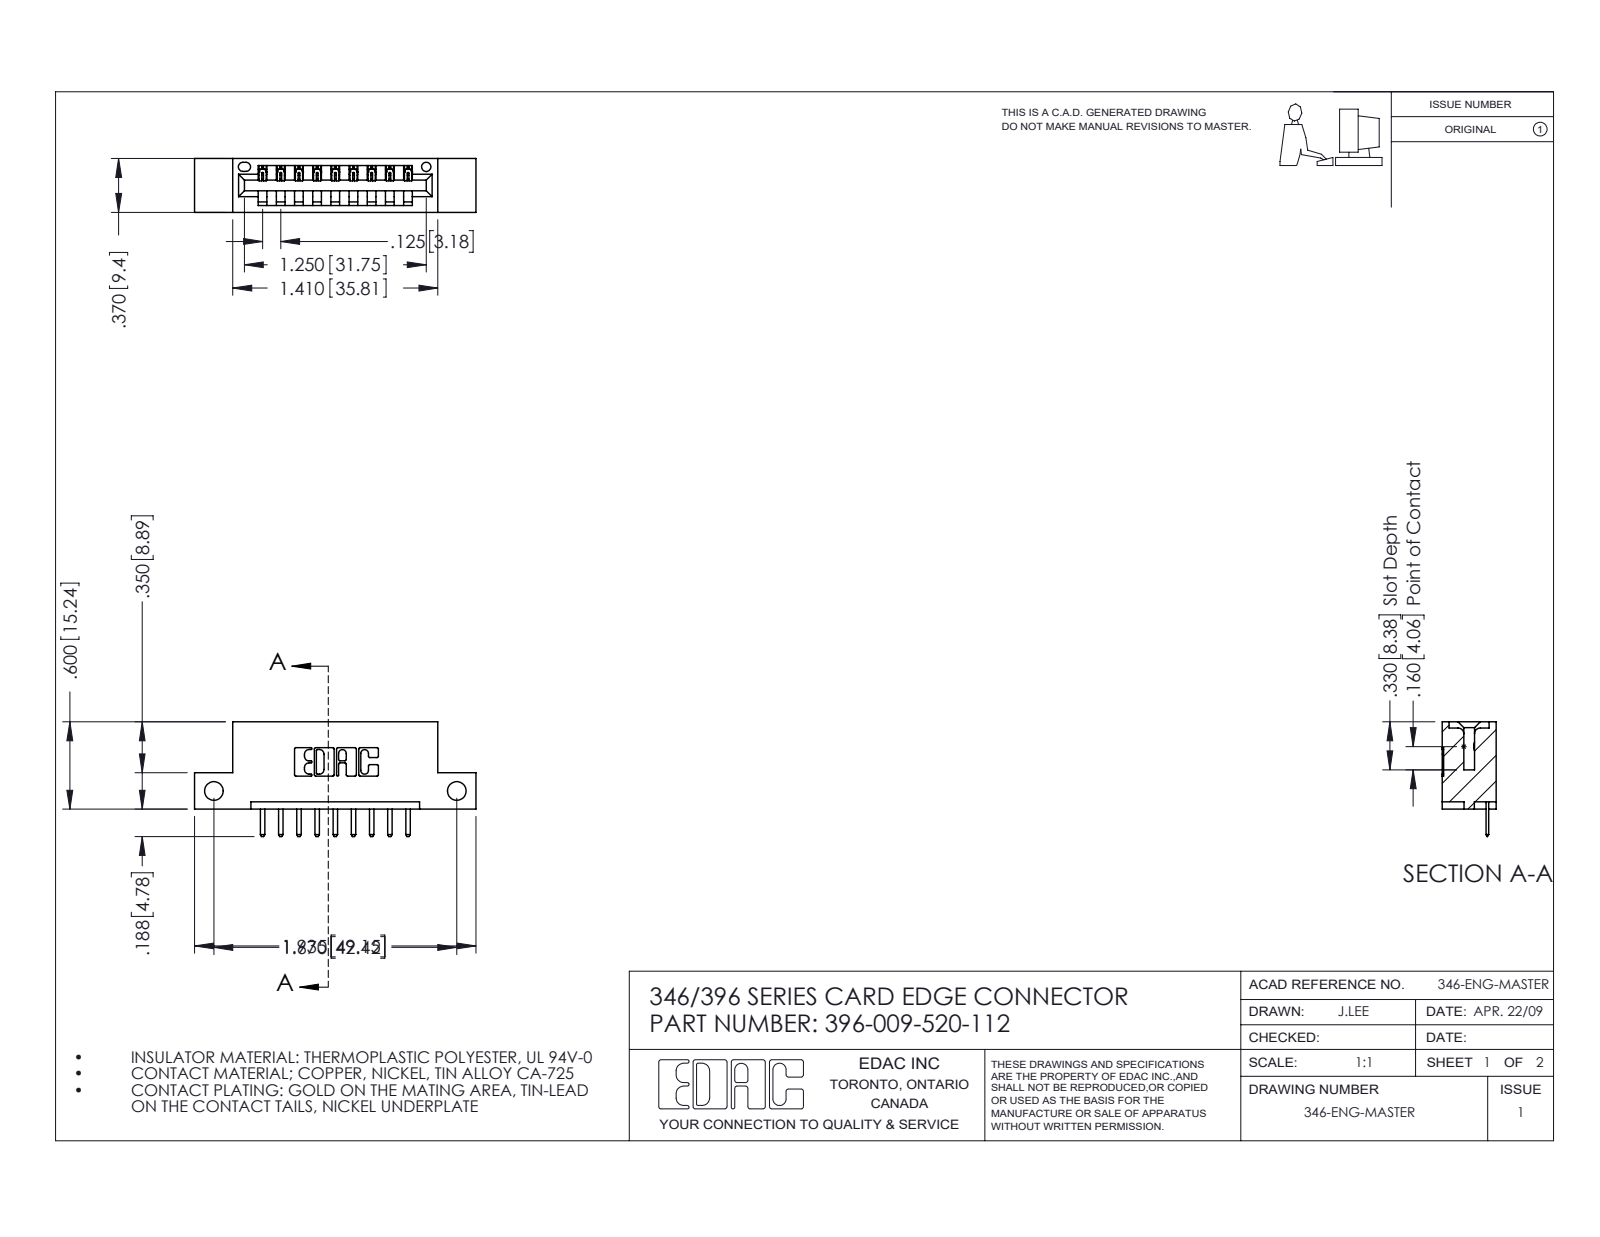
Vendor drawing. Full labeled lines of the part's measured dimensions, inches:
Part name (STEP PRODUCT): 396-009-520-112; 345-292-001_345-293-120; 346 Part_Flush Mounting Lugs - Side Mount
STEP written by: SolidWorks 2016 (CONFIG_CONTROL_DESIGN)
Units: inches
Bodies: 10 solids, 680 faces (454 planar, 226 cylindrical, 0 other)
Overall size (bounding box): 1.935 × 0.788 × 0.37
Volume: 0.266 in³ · Surface area: 7.543 in²
Round holes (diameter × count): ⌀0.128 ×2, ⌀0.064 ×1
Partial cylindrical surfaces — rounded edges, fillets, slot ends (radius × count): R0.01 ×22, R0.01 ×20, R0.006 ×18, R0.007 ×6, R0.031 ×6, R0.026 ×3, R0.031 ×2, R0.04 ×2
Main face-to-face distances: 0.25, 0.37, 0.048, 0.322, 0.148, 0.222, 0.1, 0.174, 0.125, 0.5
Hole centre spacings: 1.67
